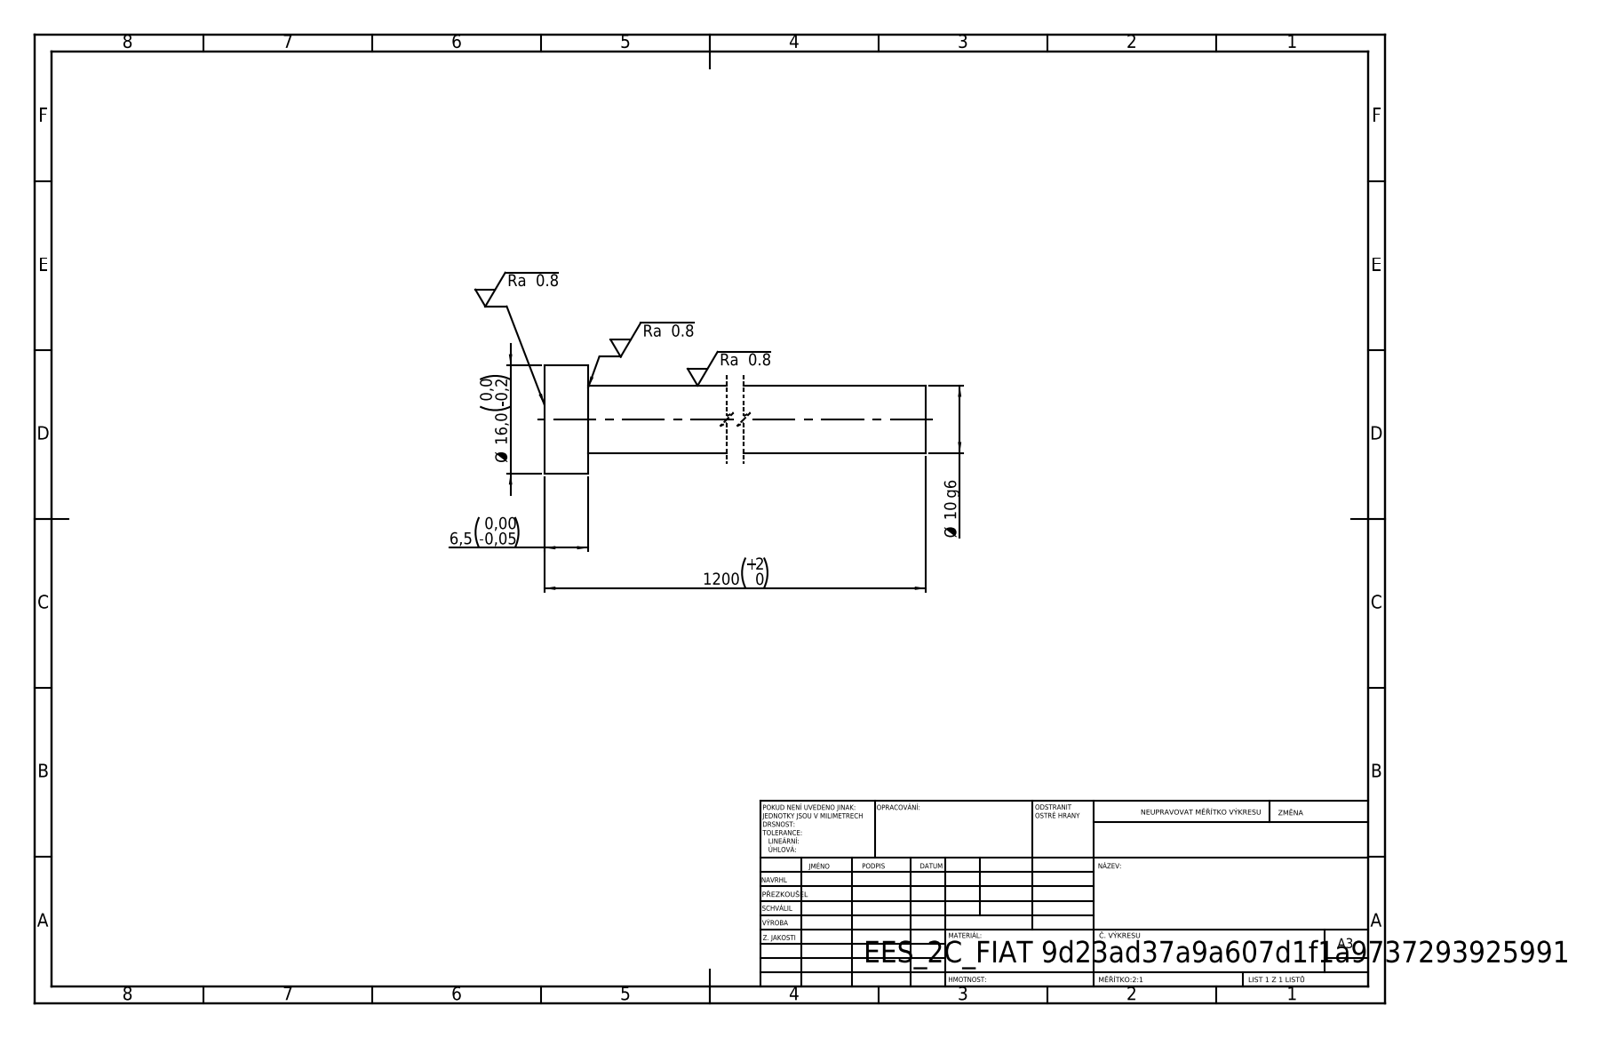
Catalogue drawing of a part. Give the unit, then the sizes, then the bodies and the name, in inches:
Units: inches
Overall size (bounding box): 47.244 × 0.63 × 0.63
Round bosses / shafts (diameter × count): ⌀0.63 ×1, ⌀0.394 ×1
Main face-to-face distances: 0.256, 47.244, 46.988
Volume: 5.8 in³ · Surface area: 59.25 in²
Bodies: 1 solid, 7 faces (3 planar, 4 cylindrical, 0 other)
STEP written by: SolidWorks 2019 (CONFIG_CONTROL_DESIGN)
